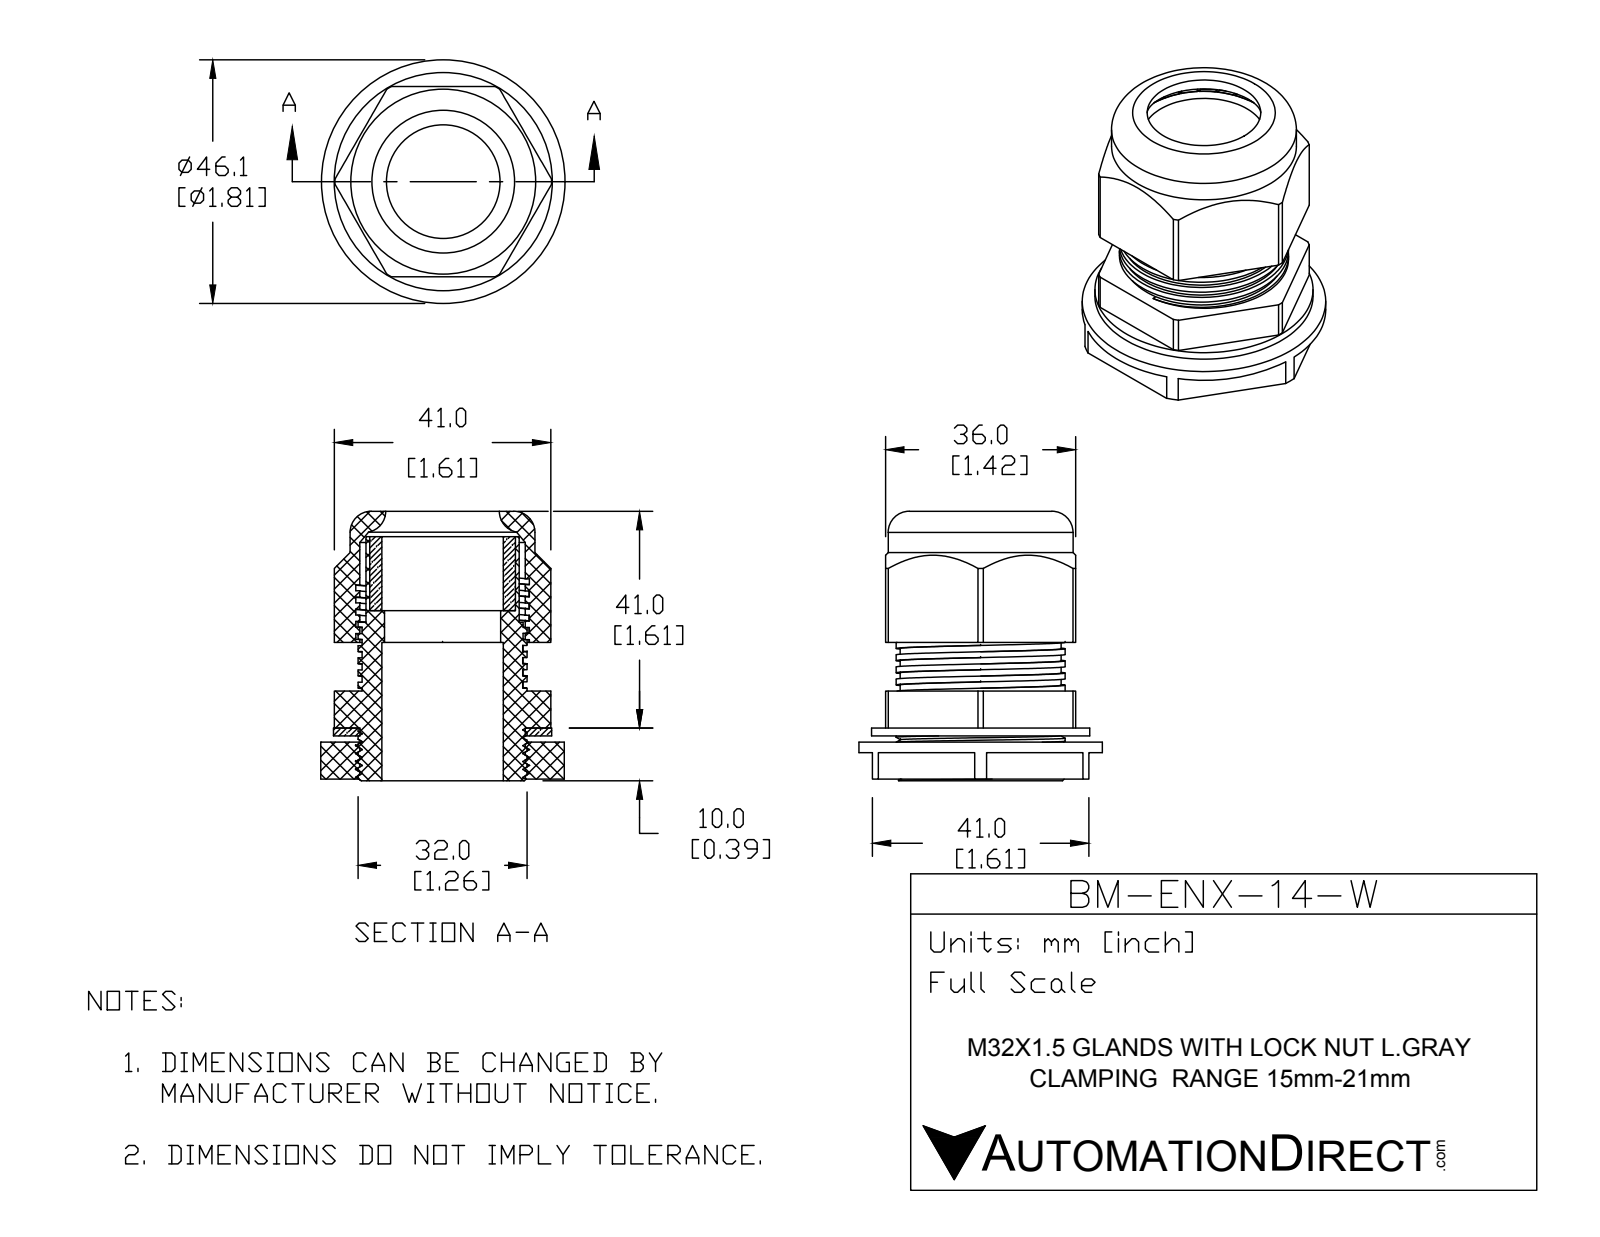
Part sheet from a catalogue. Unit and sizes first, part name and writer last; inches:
Units: inches
Overall size (bounding box): 2.008 × 1.815 × 1.815
Round holes (diameter × count): ⌀0.866 ×1, ⌀0.906 ×1, ⌀1.087 ×1, ⌀1.232 ×1, ⌀1.233 ×1
Round bosses / shafts (diameter × count): ⌀1.815 ×1, ⌀1.626 ×1, ⌀1.378 ×1, ⌀1.26 ×1, ⌀1.142 ×1
Partial cylindrical surfaces — rounded edges, fillets, slot ends (radius × count): R0.807 ×1
Main face-to-face distances: 1.417, 0.276, 0.381, 0.106, 0.335, 0.098, 1.516, 0.322, 0.046, 0.059
Volume: 1.897 in³ · Surface area: 40.62 in²
Bodies: 5 solids, 243 faces (139 planar, 83 cylindrical, 21 other)
Part name (STEP PRODUCT): BM-ENX-14-W
STEP written by: SolidWorks 2015 (CONFIG_CONTROL_DESIGN)
